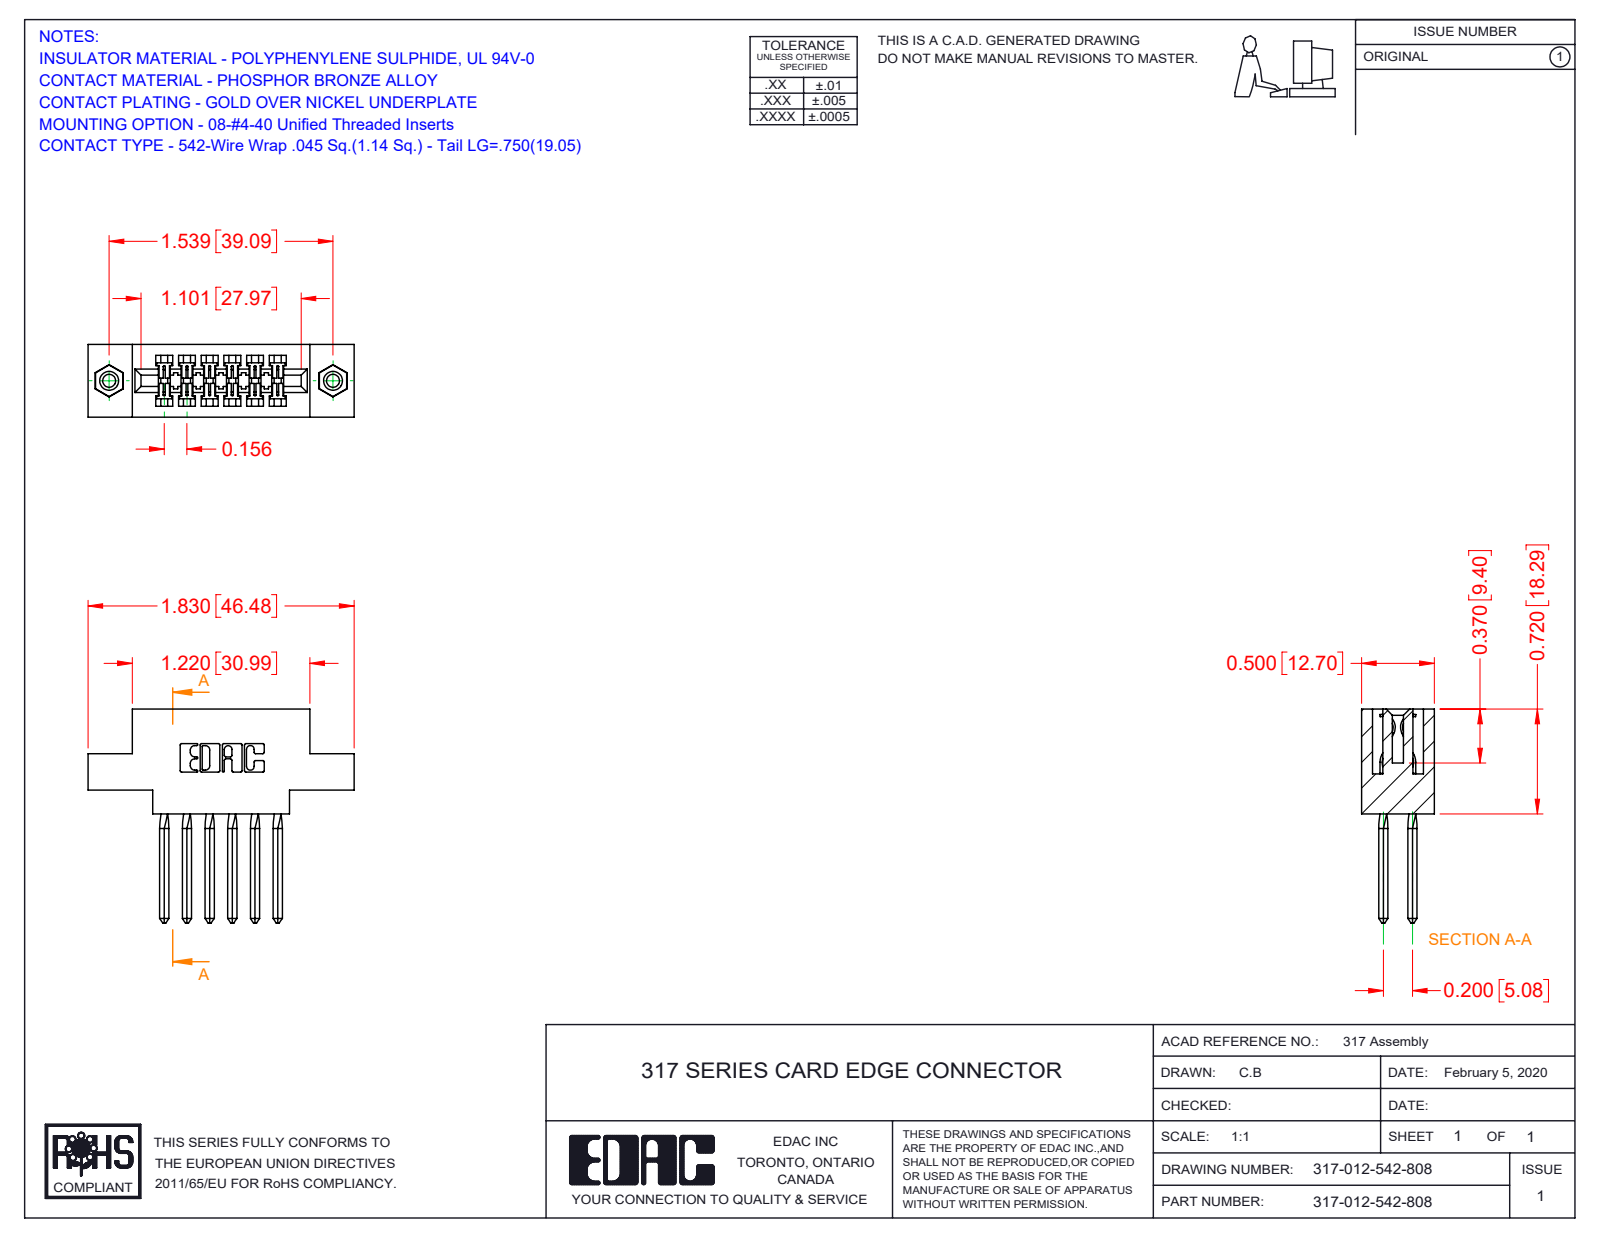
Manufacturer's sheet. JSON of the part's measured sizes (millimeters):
{"part_name": "345-250-001_345-250-003-102; 317 Part_.156 Dia - TI; 317-012-542-808; 317-290-003_542", "step_written_by": "SolidWorks 2016 (CONFIG_CONTROL_DESIGN)", "units": "millimeters", "bodies": {"solids": 15, "faces": 846, "planar": 642, "cylindrical": 140, "other": 64}, "overall_size": [46.5, 37.3, 12.7], "volume_mm3": 6470, "surface_area_mm2": 7858, "round_holes": [[2.3, 2], [3.2, 2], [4, 2]], "round_bosses_or_shafts": [[3.9, 2]], "partial_cylinders_radius": [[0.2, 24], [0.3, 22], [0.2, 6], [0.8, 6], [0.7, 3], [1.9, 2], [2.3, 2], [2.5, 2]], "face_to_face_distances": [12.7, 2.8, 1.9, 10.8, 5.6, 1.7, 2.9, 4, 1.1, 4.1], "hole_center_spacings": [39.1]}
